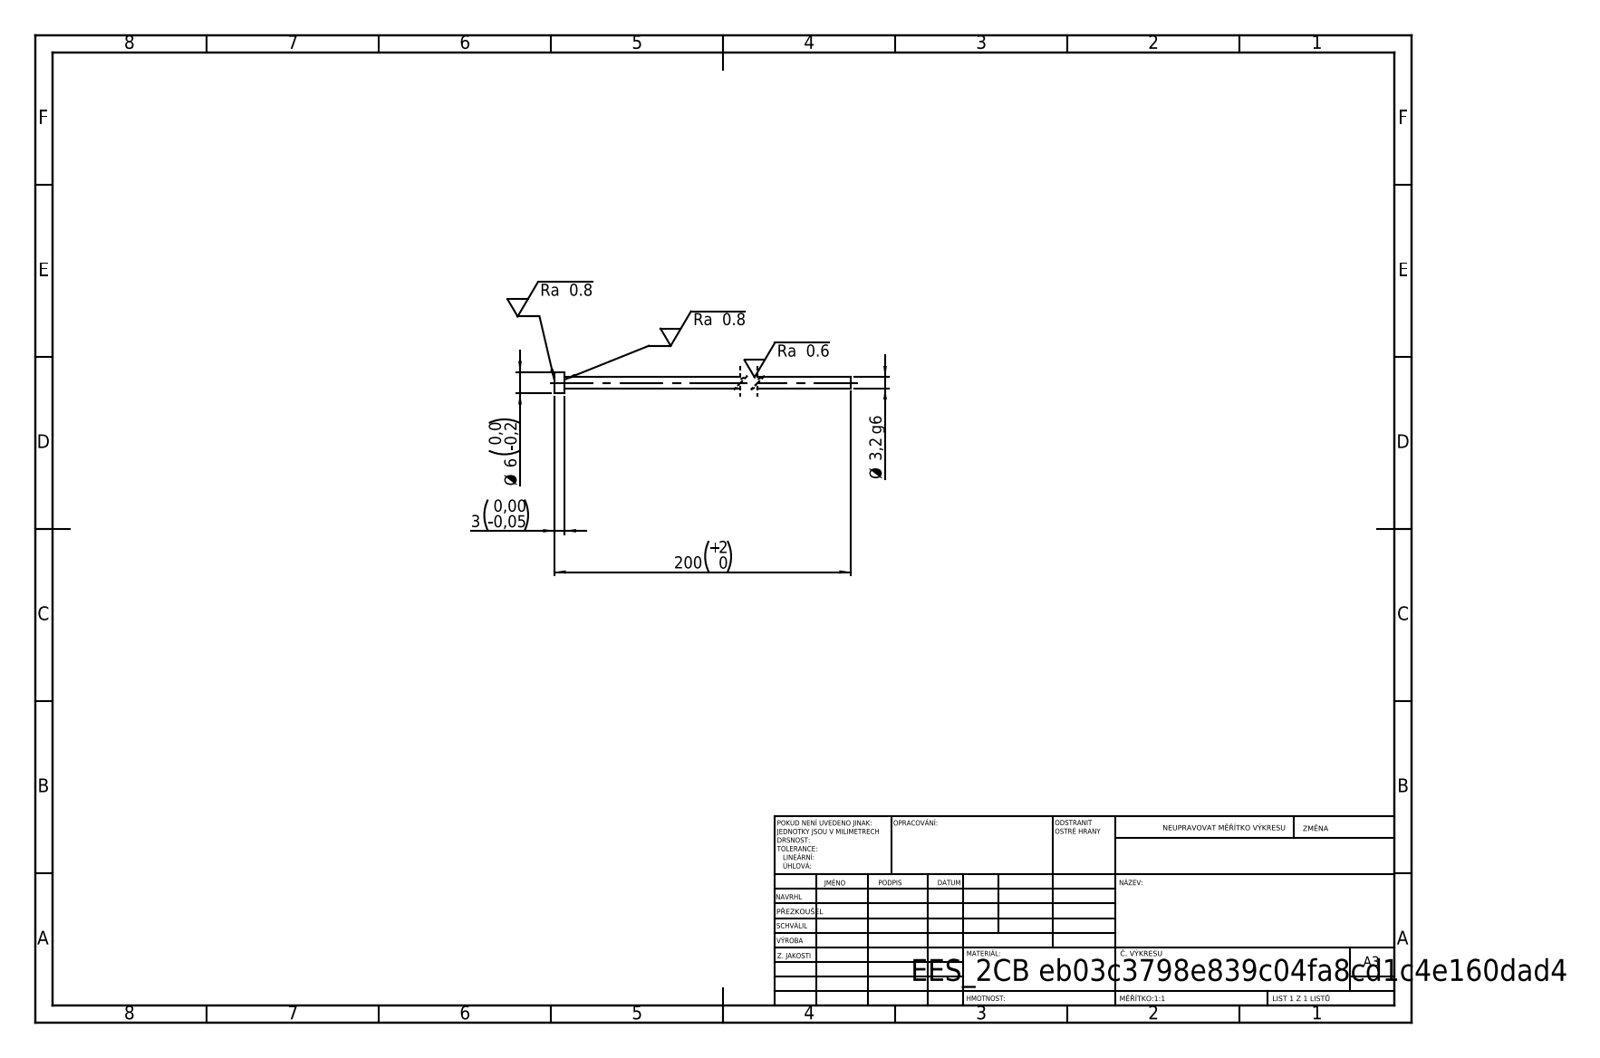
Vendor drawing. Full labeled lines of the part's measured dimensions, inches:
STEP written by: SolidWorks 2019 (CONFIG_CONTROL_DESIGN)
Units: inches
Bodies: 1 solid, 7 faces (3 planar, 4 cylindrical, 0 other)
Overall size (bounding box): 7.874 × 0.236 × 0.236
Volume: 0.102 in³ · Surface area: 3.246 in²
Round bosses / shafts (diameter × count): ⌀0.236 ×1, ⌀0.126 ×1
Main face-to-face distances: 0.118, 7.874, 7.756
